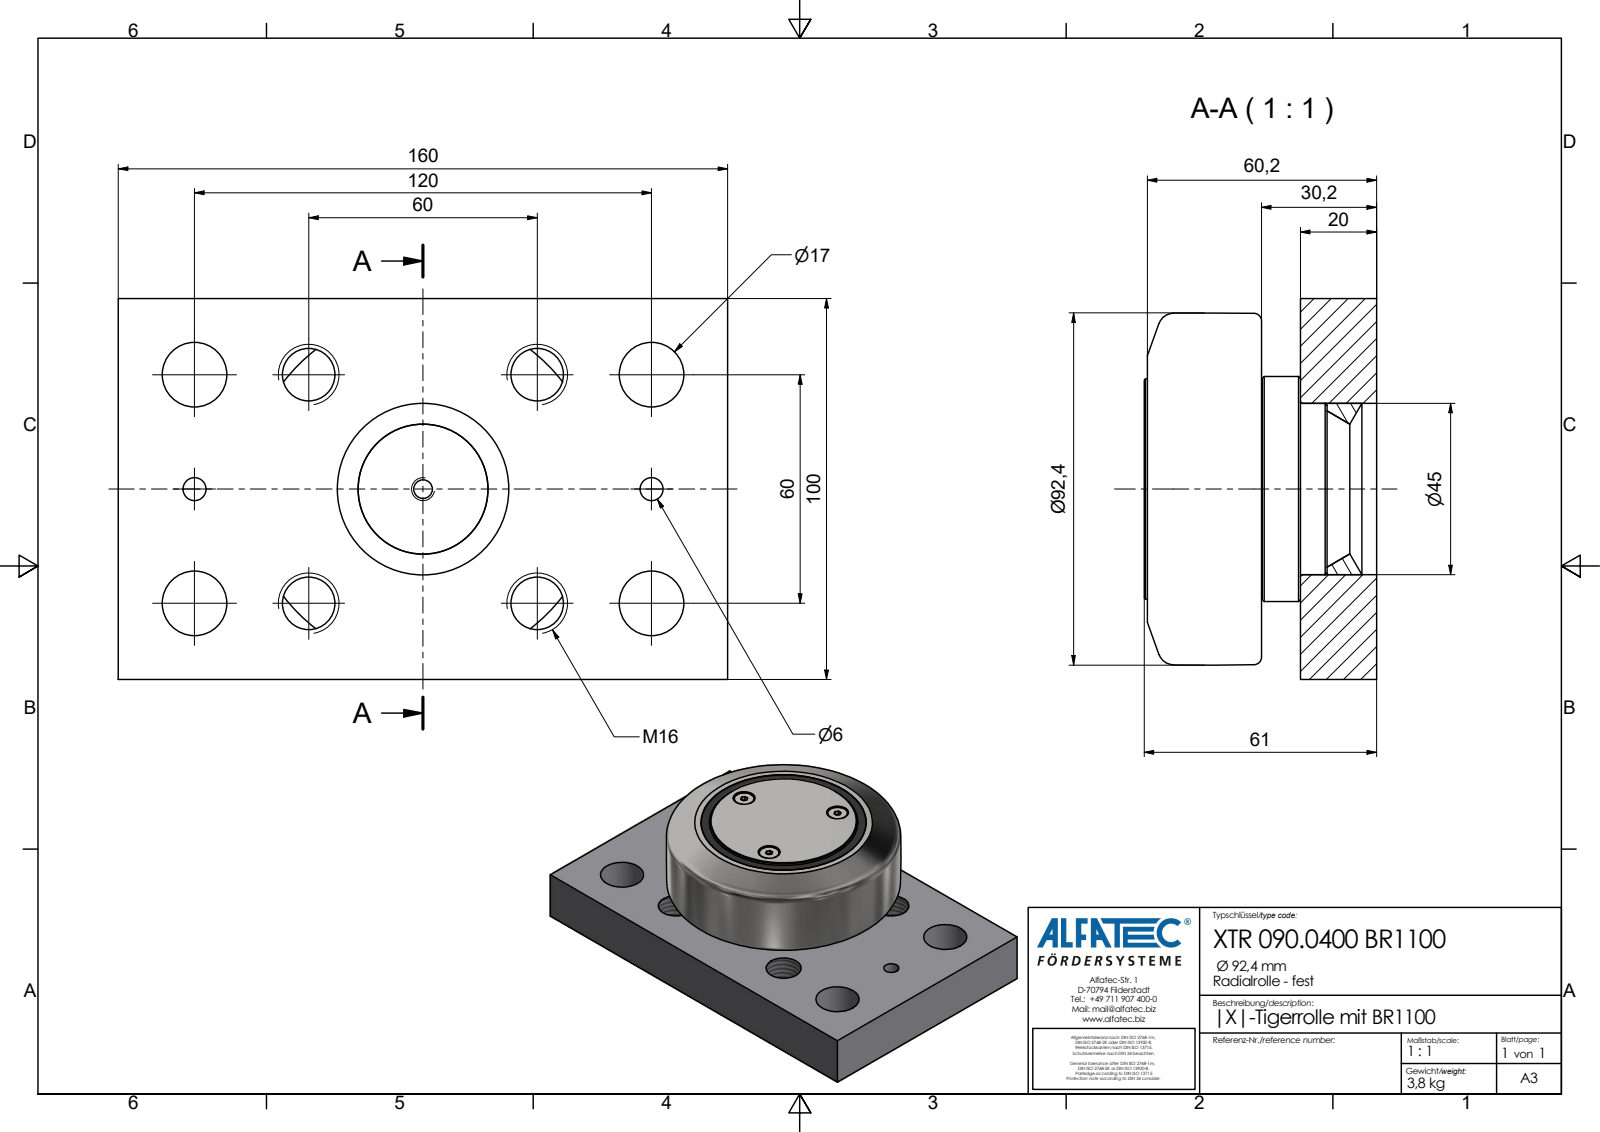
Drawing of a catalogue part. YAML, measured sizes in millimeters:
part_name: "XTR 090.0400 BR1100_Kontur"
step_written_by: "Autodesk Inventor 2020 (AP242_MANAGED_MODEL_BASED_3D_ENGINEERING_MIM_LF)"
units: millimeters
bodies: {solids: 1, faces: 71, planar: 39, cylindrical: 21, other: 11}
overall_size: [160, 100, 61]
volume: 502153
surface_area: 66756
round_holes:
  - {diameter: 13.84, count: 4}
  - {diameter: 17, count: 4}
  - {diameter: 8.6, count: 3}
  - {diameter: 6, count: 2}
  - {diameter: 4.92, count: 1}
  - {diameter: 45, count: 1}
round_bosses_or_shafts:
  - {diameter: 7.8, count: 3}
  - {diameter: 59, count: 1}
  - {diameter: 57.8, count: 1}
  - {diameter: 55.3, count: 1}
face_to_face_distances: [20, 30.2, 10.2, 100, 61, 41, 30.8, 160, 30, 60.2]
hole_center_spacings: [30, 42.43, 60, 67.08, 90, 94.87, 108.17, 123.69]
